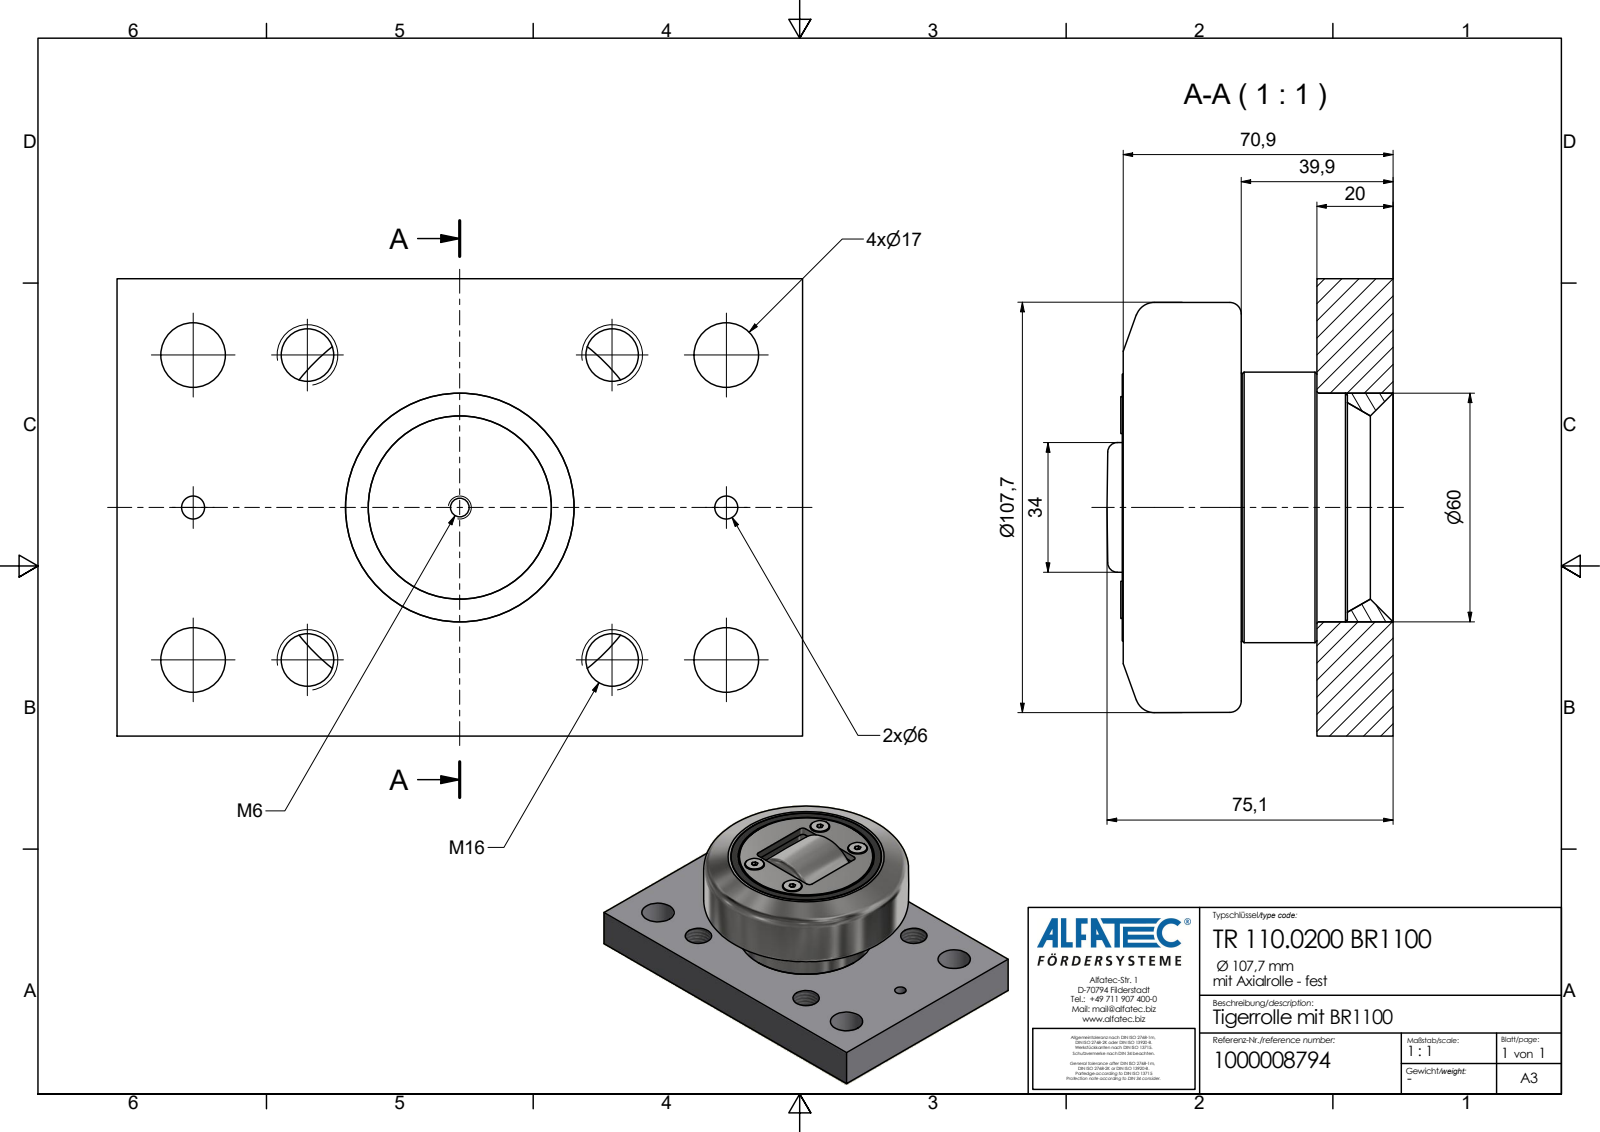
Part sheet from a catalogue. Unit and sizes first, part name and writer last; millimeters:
Units: millimetres
Overall size (bounding box): 180 × 120 × 75.1
Round holes (diameter × count): ⌀13.84 ×4, ⌀17 ×4, ⌀6 ×2
Round bosses / shafts (diameter × count): ⌀9.75 ×4, ⌀71 ×1, ⌀70.5 ×1
Partial cylindrical surfaces — rounded edges, fillets, slot ends (radius × count): R2 ×4
Main face-to-face distances: 20, 39.9, 19.9, 120, 180, 71.1, 51.1, 31.2, 70.9, 50.9
Hole centre spacings: 80, 30, 40, 50, 85.44, 110, 117.05, 136.01
Volume: 753 747 mm³ · Surface area: 84 293 mm²
Bodies: 1 solid, 87 faces (53 planar, 20 cylindrical, 14 other)
Part name (STEP PRODUCT): TR 110.0200 BR1100_Kontur
STEP written by: Autodesk Inventor 2020 (AP242_MANAGED_MODEL_BASED_3D_ENGINEERING_MIM_LF)
